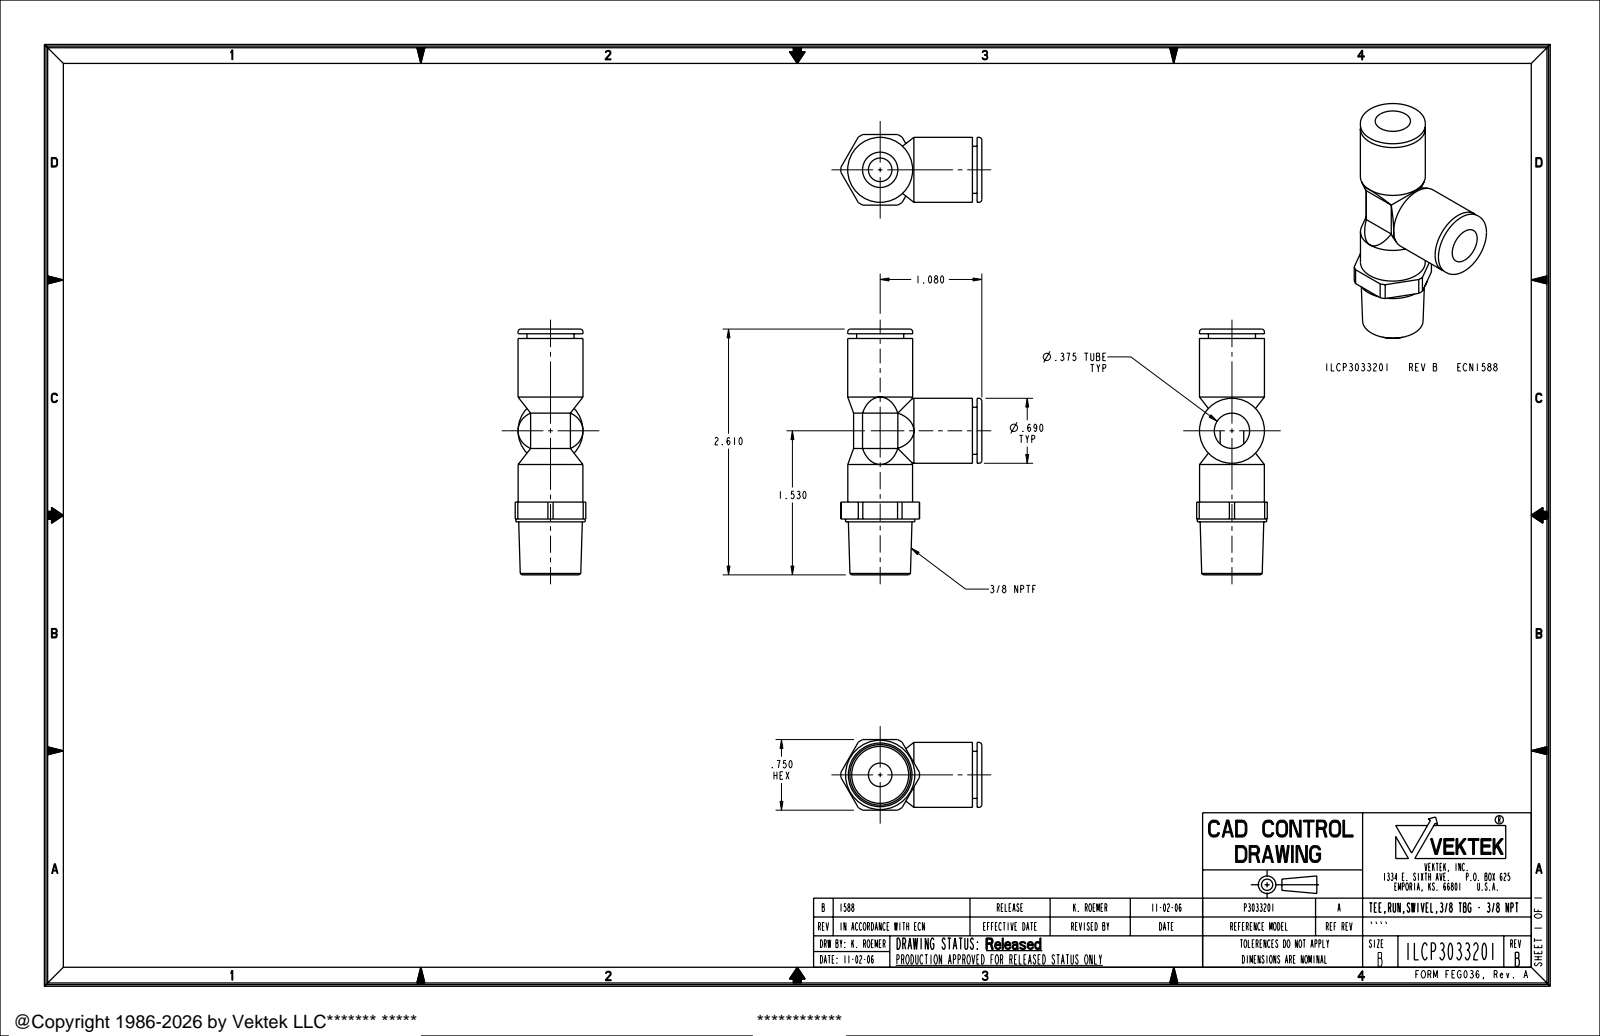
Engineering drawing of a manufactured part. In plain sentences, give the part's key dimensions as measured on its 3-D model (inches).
The part is named "ILCP3033201". Its 3-D file was written by "PRO/ENGINEER BY PARAMETRIC TECHNOLOGY CORPORATION, 2005180 (AUTOMOTIVE_DESIGN_CC2)". It is 1 solid with 72 faces: 27 planar, 31 cylindrical and 14 other. Overall it measures 2.61 by 1.498 by 0.75 inches. Its volume is 0.875 cubic inches and its surface area 12.23 square inches. Round holes: 2 of diameter 0.375, 1 of diameter 0.25. Round bosses or shafts: 2 of diameter 0.69, 2 of diameter 0.5, 1 of diameter 0.736, 1 of diameter 0.688. Partial cylindrical surfaces (rounded edges, fillets, slot ends): 1 of radius 0.282, 1 of radius 0.418. The main face-to-face distances are 0.05, 0.1, 2.61, 0.75, 2.56, 2.51, 0.423, 0.163, 0.586, 0.773.
